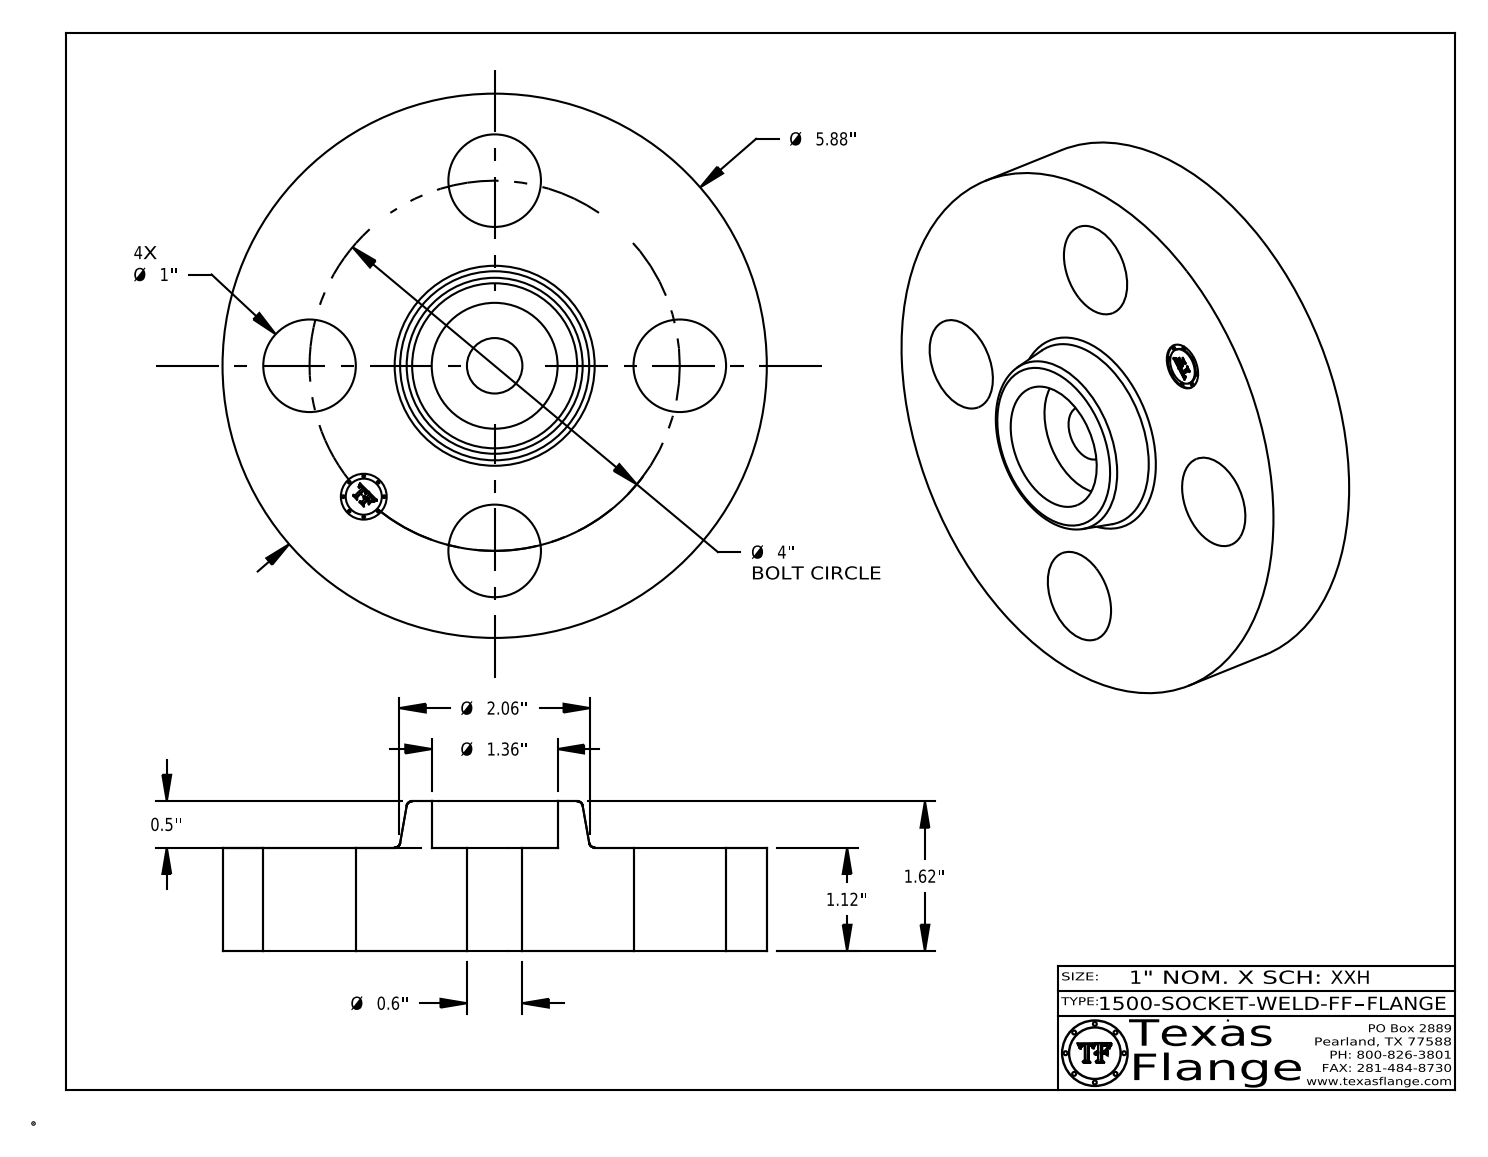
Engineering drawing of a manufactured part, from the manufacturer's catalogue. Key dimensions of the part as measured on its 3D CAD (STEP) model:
Part name (STEP PRODUCT): 1500-SOCKET-WELD-FF
STEP written by: CATIA V5 STEP AP214 (AUTOMOTIVE_DESIGN)
Units: inches
Bodies: 1 solid, 409 faces (369 planar, 34 cylindrical, 6 other)
Overall size (bounding box): 5.88 × 5.88 × 1.62
Volume: 27.38 in³ · Surface area: 88.95 in²
Round holes (diameter × count): ⌀1 ×4, ⌀0.495 ×1, ⌀0.599 ×1, ⌀1.36 ×1
Round bosses / shafts (diameter × count): ⌀0.03 ×8, ⌀5.88 ×1, ⌀0.39 ×1
Main face-to-face distances: 1.12, 1.62, 0.5, 0.015, 1.105, 0.515, 0.148, 0.145, 0.027, 0.096
Hole centre spacings: 2, 2.828, 1.531, 3.695, 4
